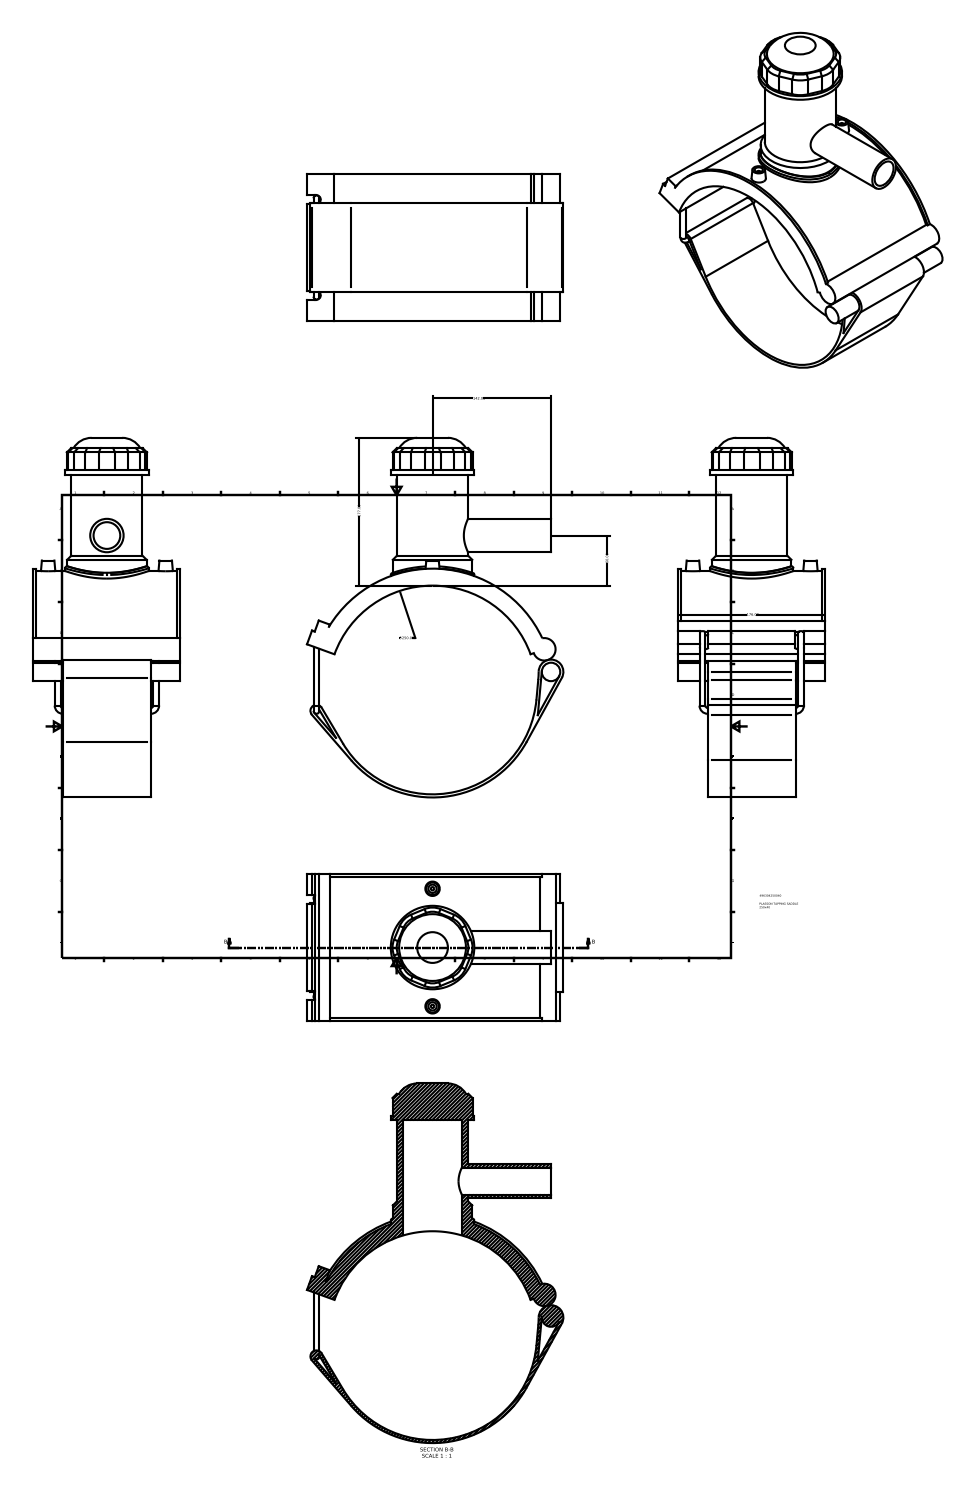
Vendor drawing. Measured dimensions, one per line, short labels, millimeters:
name: 496304250040
written by: Autodesk Inventor 2015 (AUTOMOTIVE_DESIGN)
unit: mm
bodies: 1 solid, 121 faces (68 planar, 38 cylindrical, 15 other)
size: 430.75 × 307.08 × 176
volume: 1 973 000 mm³; area: 387 493 mm²
holes: 2× ⌀10, 1× ⌀32, 1× ⌀70
bosses: 2× ⌀7, 2× ⌀4, 1× ⌀100, 1× ⌀95, 1× ⌀85, 1× ⌀40, 1× ⌀22.12
rounds: 8× R25, 2× R5.25, 2× R125, 1× R3.5, 1× R7.25, 1× R13.46, 1× R14.81, 1× R128.75
face distances: 3.75, 176, 3.78, 35.2, 140.8, 17.5, 14, 3.34, 31.51, 3.5
hole spacings: 70.4, 140.8
